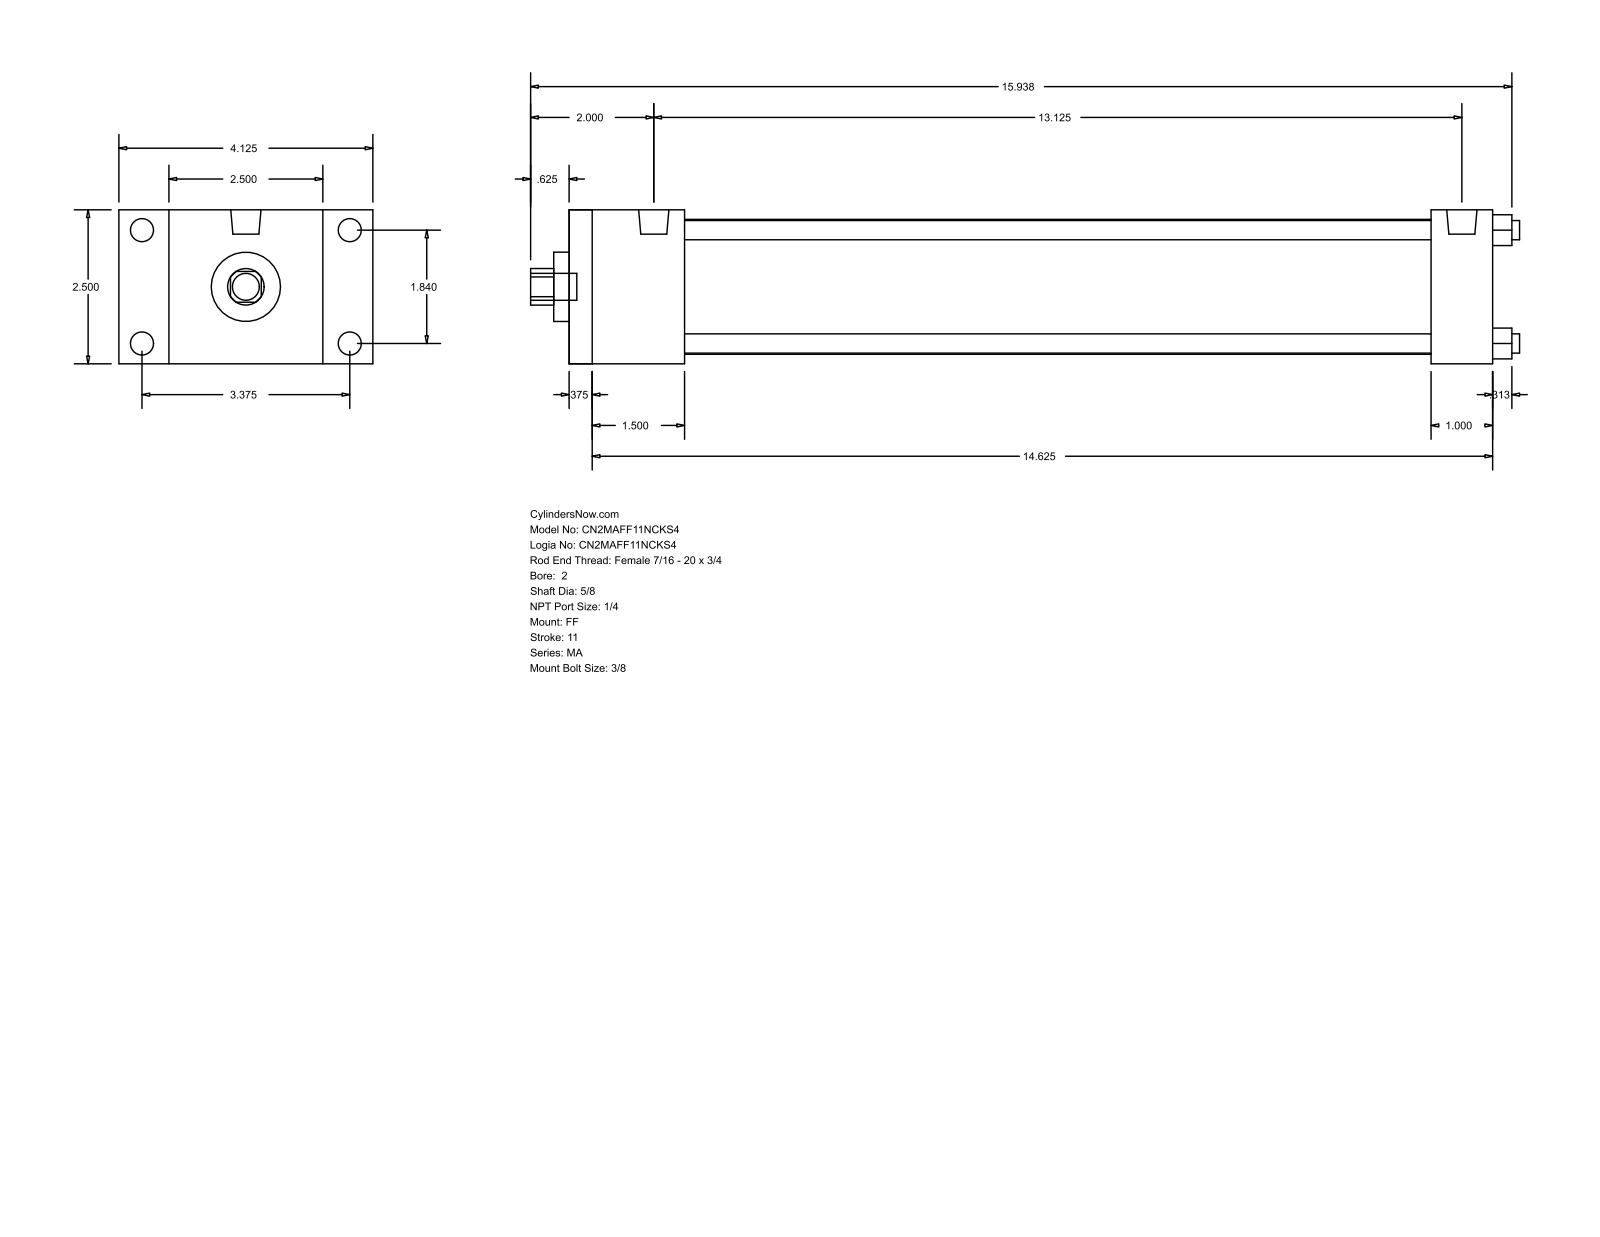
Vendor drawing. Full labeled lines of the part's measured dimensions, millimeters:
Part name (STEP PRODUCT): MA_FF__0200_0.625
STEP written by: GSSL Pune (CONFIG_CONTROL_DESIGN)
Units: millimetres
Bodies: 0 solids, 92 faces (64 planar, 28 cylindrical, 0 other)
Overall size (bounding box): 407.99 × 104.78 × 63.5
Round holes (diameter × count): ⌀7.94 ×4, ⌀15.88 ×1, ⌀28.57 ×1, ⌀55.63 ×1
Round bosses / shafts (diameter × count): ⌀9.53 ×4, ⌀7.94 ×4, ⌀12.49 ×2, ⌀11.11 ×1
Partial cylindrical surfaces — rounded edges, fillets, slot ends (radius × count): R7.54 ×1
Main face-to-face distances: 63.5, 381, 9.52, 371.48, 25.4, 38.1, 47.62, 355.6, 346.08, 307.98
Hole centre spacings: 33.05, 46.74, 66.1
